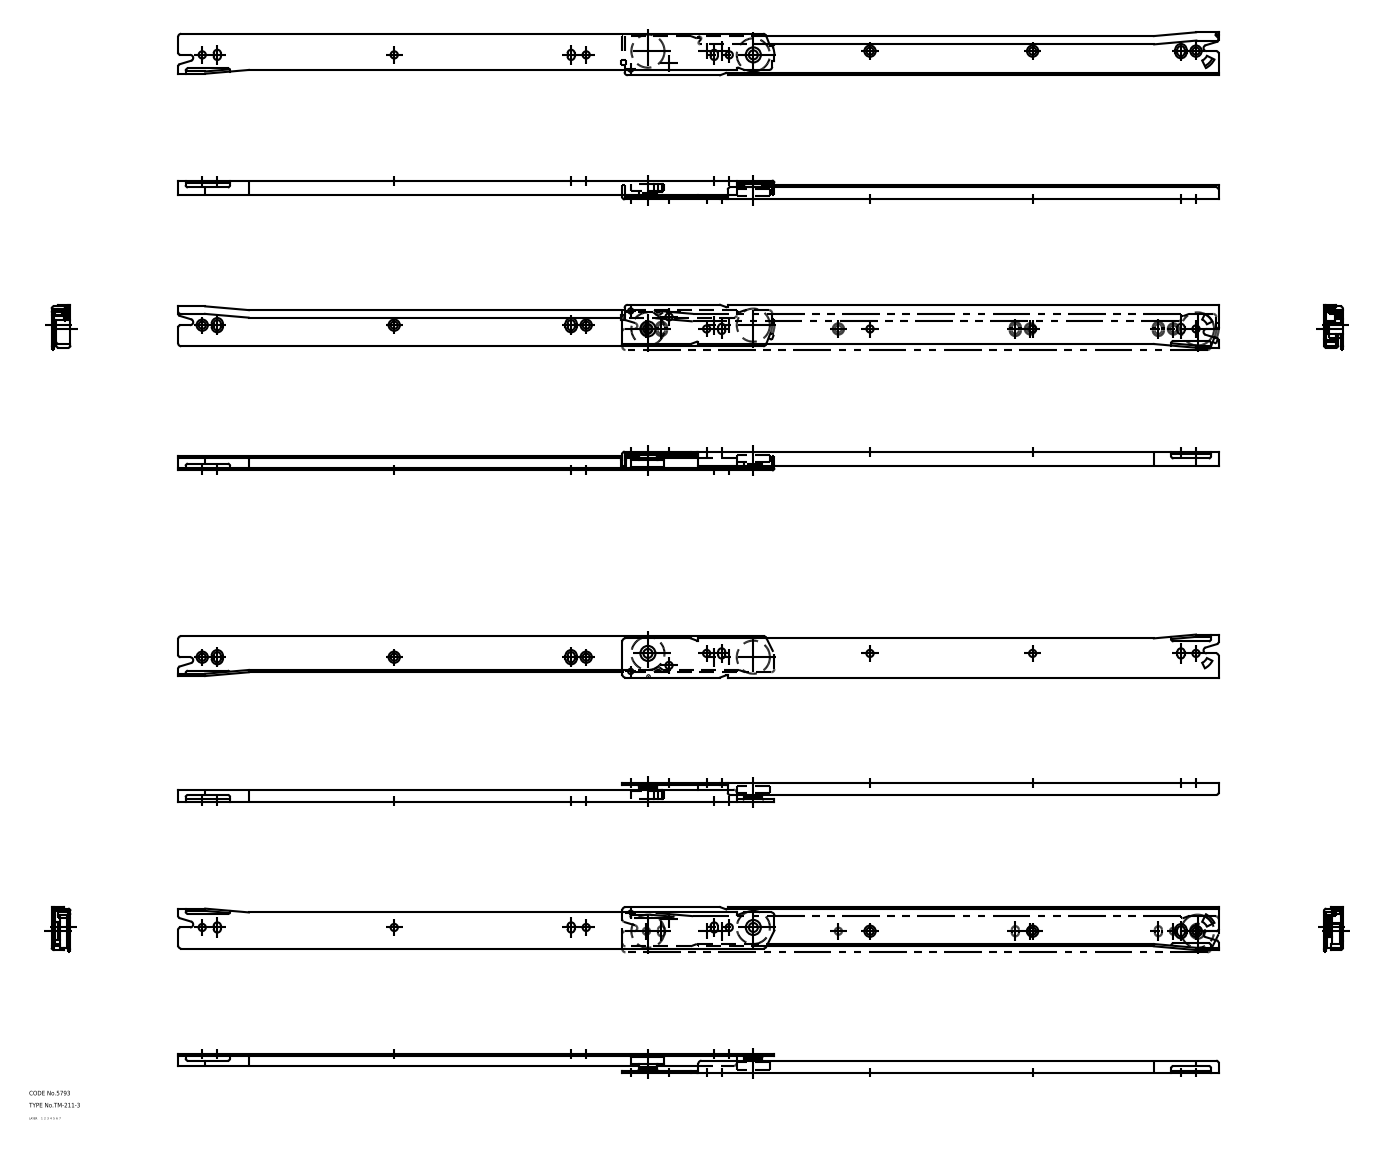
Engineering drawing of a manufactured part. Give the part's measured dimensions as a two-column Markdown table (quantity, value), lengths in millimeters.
| quantity | value |
| --- | --- |
| part name | roller; member_B; member_A; TM_211_3_1132_36 |
| STEP written by | CADfix (AUTOMOTIVE_DESIGN) |
| units | millimeters |
| bodies | 4 solids, 181 faces (0 planar, 0 cylindrical, 181 other) |
| overall size | 691 × 28.5 × 12.5 |
| volume | 42 789 mm³ |
| surface area | 56 956 mm² |
